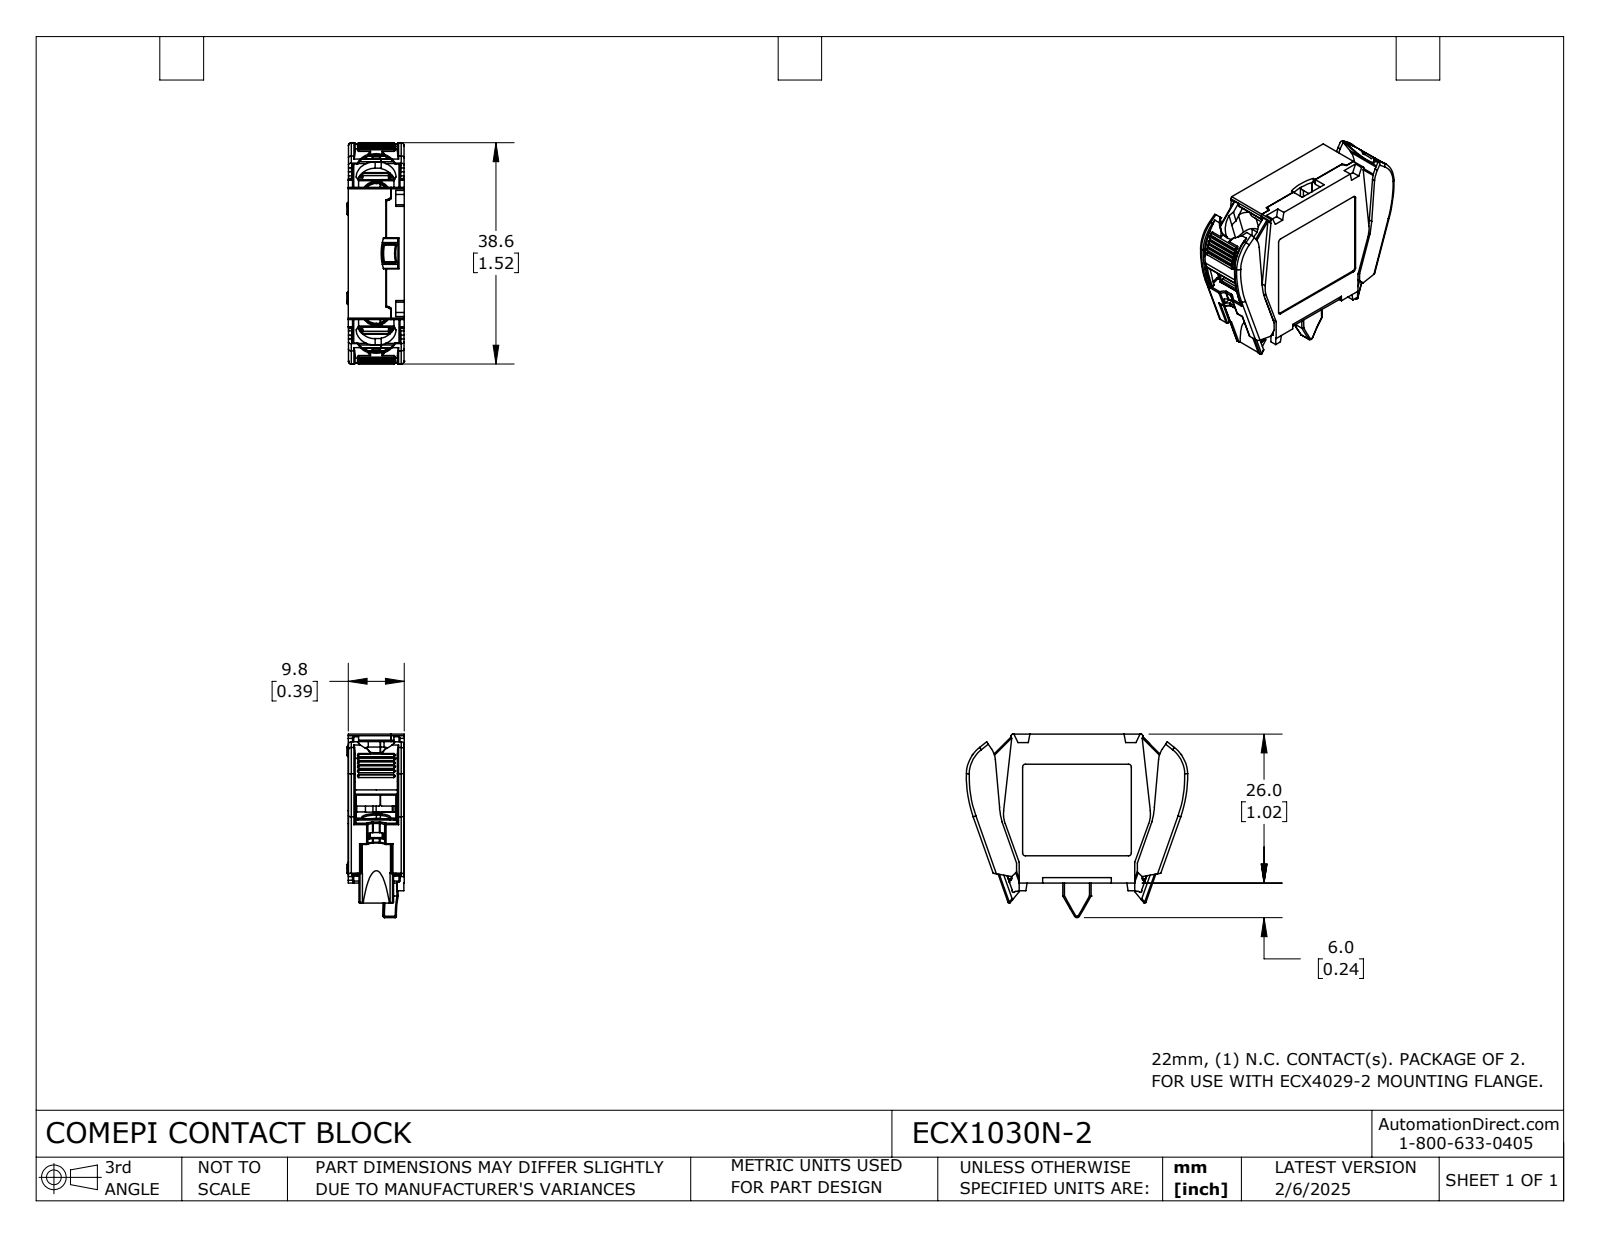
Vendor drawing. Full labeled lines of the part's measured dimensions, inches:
Part name (STEP PRODUCT): ECX1030N-2
STEP written by: SolidWorks 2024 (CONFIG_CONTROL_DESIGN)
Units: inches
Bodies: 5 solids, 1545 faces (815 planar, 491 cylindrical, 239 other)
Overall size (bounding box): 1.521 × 1.261 × 0.396
Volume: 0.246 in³ · Surface area: 13.35 in²
Round holes (diameter × count): ⌀0.079 ×4, ⌀0.096 ×4, ⌀0.117 ×4
Round bosses / shafts (diameter × count): ⌀0.094 ×4, ⌀0.075 ×4
Partial cylindrical surfaces — rounded edges, fillets, slot ends (radius × count): R0.008 ×109, R0.012 ×24, R0.006 ×18, R0.02 ×16, R0.004 ×14, R0.01 ×12, R0.005 ×10, R0.008 ×10
Main face-to-face distances: 0.028, 0.053, 0.319, 0.378, 0.03, 0.059, 0.325, 0.327, 0.323, 0.384
Hole centre spacings: 0.807, 1.014, 0.598, 0.63
